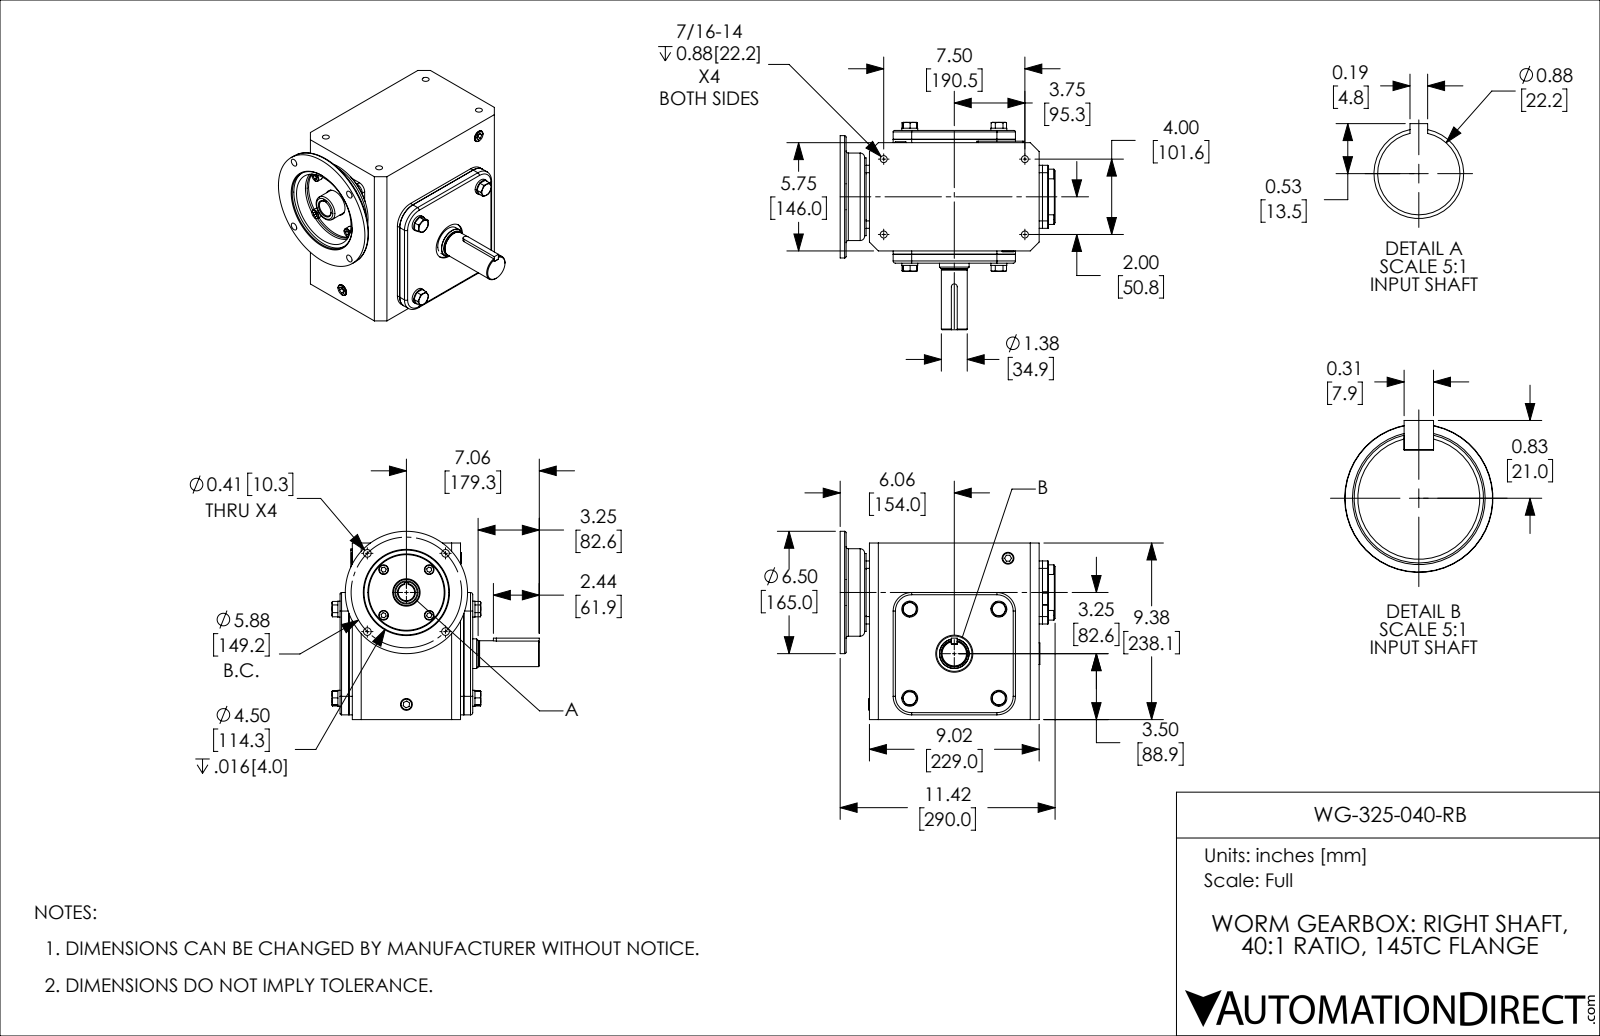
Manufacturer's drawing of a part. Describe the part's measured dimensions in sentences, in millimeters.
The part is named "WG-325-040-RB". Its 3-D file was written by "SolidWorks 2017 (AUTOMOTIVE_DESIGN)". It is 39 solids with 576 faces: 318 planar, 168 cylindrical and 90 other. Overall it measures 290 by 279.8 by 253.9 millimeters. Its volume is 8 259 000 cubic millimeters and its surface area 582 200 square millimeters. Round holes: 4 of diameter 9.3, 4 of diameter 10.3, 3 of diameter 16, 1 of diameter 15, 1 of diameter 22.2, 1 of diameter 24.8, 1 of diameter 30, 1 of diameter 37, 1 of diameter 50, 1 of diameter 62, 1 of diameter 70, 1 of diameter 102. Round bosses or shafts: 4 of diameter 21.5, 4 of diameter 13, 1 of diameter 165, 1 of diameter 118, 1 of diameter 105, 1 of diameter 72, 1 of diameter 40, 1 of diameter 35. Partial cylindrical surfaces (rounded edges, fillets, slot ends): 11 of radius 2, 4 of radius 3, 4 of radius 10, 4 of radius 23, 4 of radius 25, 2 of radius 0.5, 2 of radius 1, 1 of radius 4. The main face-to-face distances are 2, 4.5, 165, 10, 177, 12, 167, 162.5, 14.5, 16.5. The hole center spacings are 74.6, 105.5, 60.6, 101.6, 111.5, 145.2, 147.8, 149.2.
